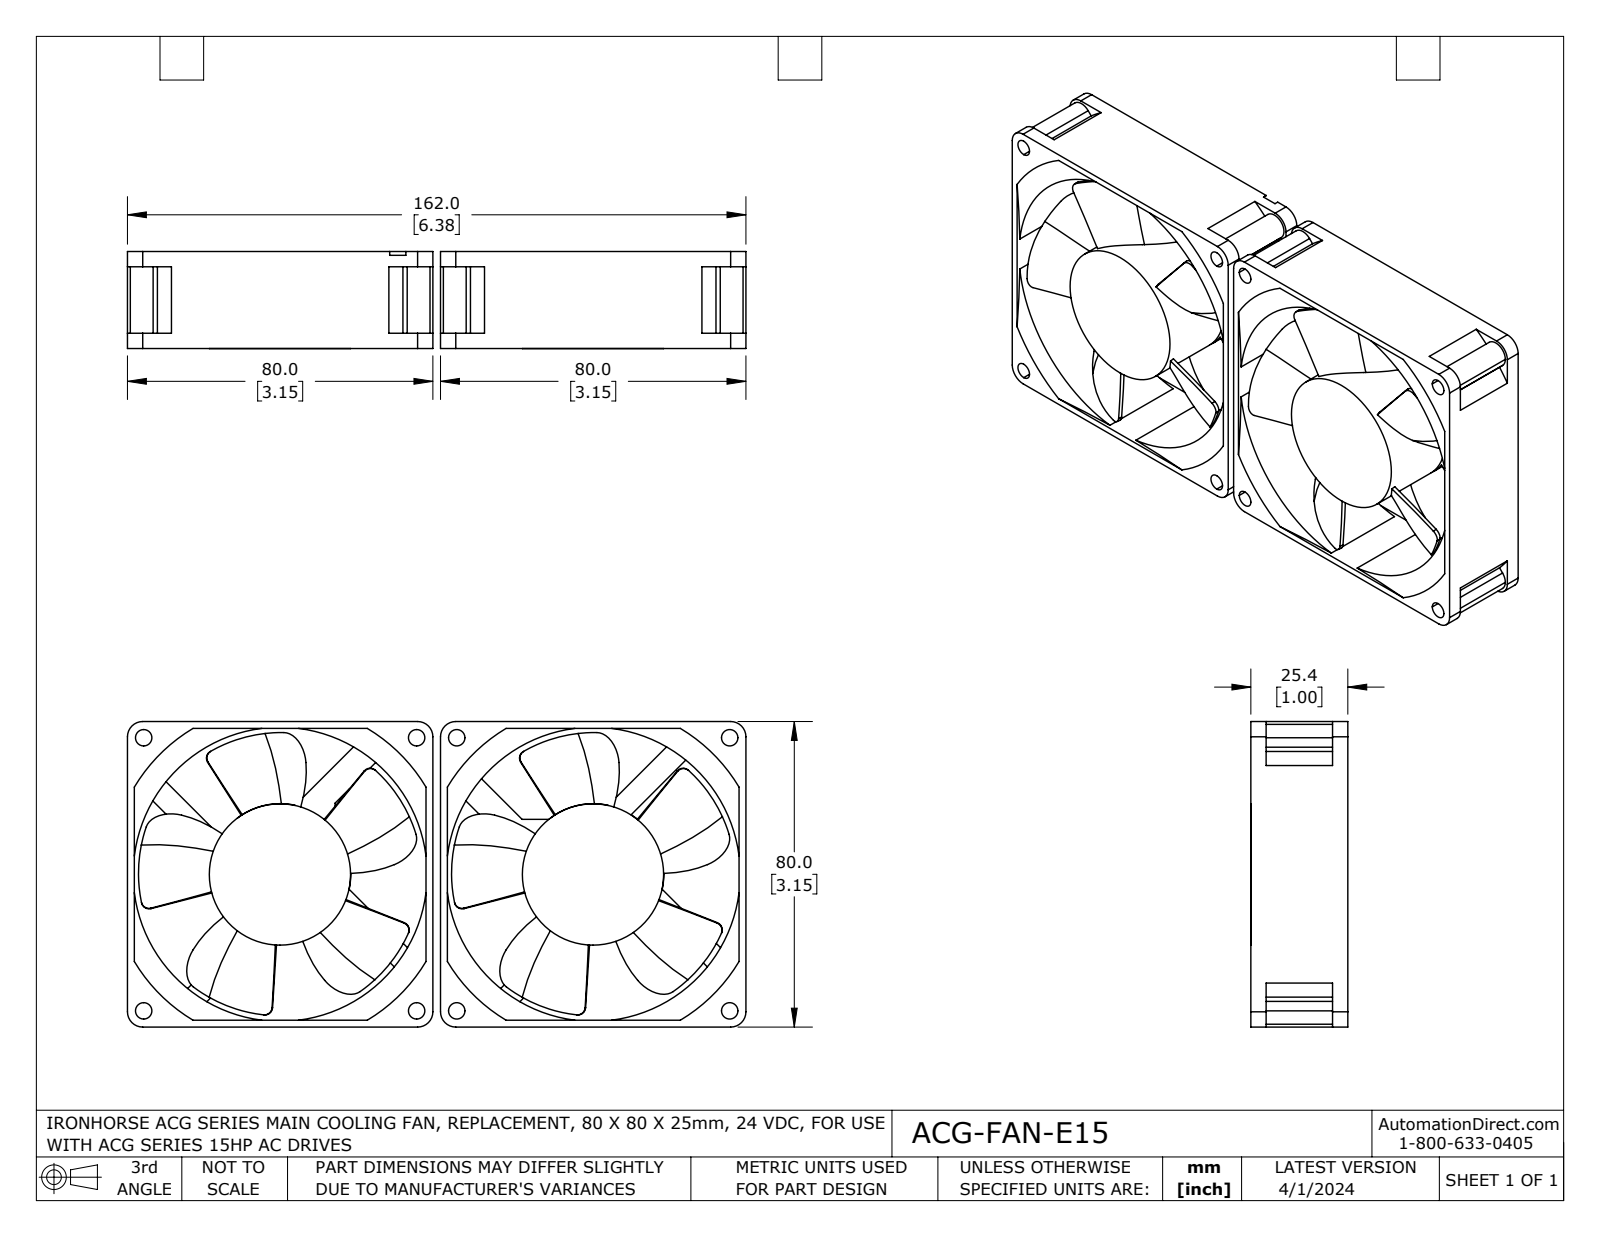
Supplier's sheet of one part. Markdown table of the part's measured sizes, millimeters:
| quantity | value |
| --- | --- |
| part name | ACG-FAN-E15 |
| STEP written by | SolidWorks 2021 (AUTOMOTIVE_DESIGN) |
| units | millimeters |
| bodies | 4 solids, 308 faces (86 planar, 108 cylindrical, 114 other) |
| overall size | 162 × 80 × 25.4 |
| volume | 135 500 mm³ |
| surface area | 66 840 mm² |
| round holes (diameter × count) | 4.3 × 8, 34 × 2, 77 × 2 |
| round bosses / shafts (diameter × count) | 37 × 2 |
| partial cylindrical surfaces (radius × count) | 2 × 10, 3.5 × 8, 4 × 8, 18 × 2, 18.5 × 2, 49.1 × 2 |
| main face-to-face distances | 80, 82, 20, 1.8, 78.2, 5.4, 25.4, 1, 4.4, 24.4 |
| hole center spacings | 50.6, 71.5, 82, 58.5, 101.1, 108.8, 123.1, 10.5 |
